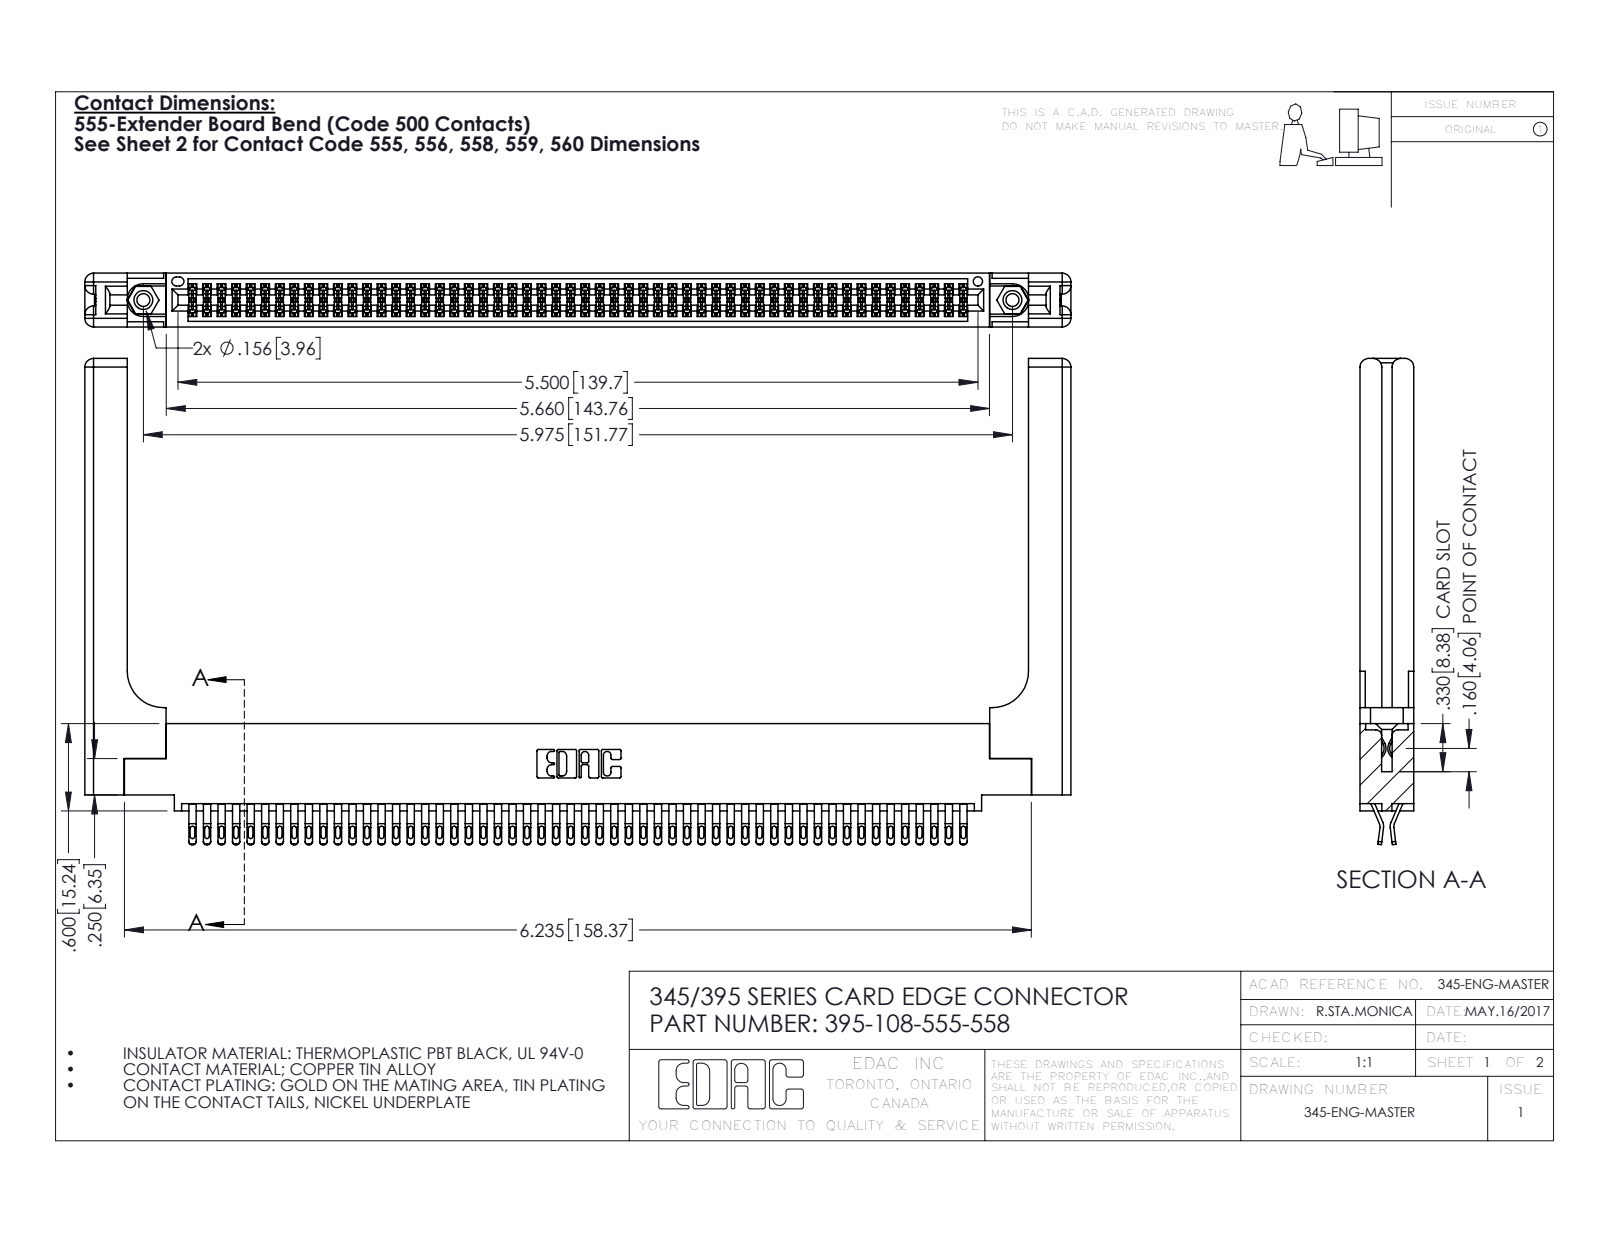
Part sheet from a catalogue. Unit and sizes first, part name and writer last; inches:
Units: inches
Overall size (bounding box): 6.779 × 3.342 × 0.37
Round holes (diameter × count): ⌀0.089 ×2, ⌀0.125 ×2, ⌀0.156 ×2, ⌀0.064 ×1
Round bosses / shafts (diameter × count): ⌀0.155 ×2
Partial cylindrical surfaces — rounded edges, fillets, slot ends (radius × count): R0.016 ×270, R0.02 ×216, R0.006 ×162, R0.01 ×22, R0.06 ×16, R0.007 ×6, R0.031 ×6, R0.026 ×3
Main face-to-face distances: 0.072, 0.298, 0.37, 0.025, 0.098, 0.272, 0.2, 0.225, 0.148, 0.15
Hole centre spacings: 0.27, 5.739, 5.975
Volume: 1.559 in³ · Surface area: 49.16 in²
Bodies: 113 solids, 6434 faces (3580 planar, 2794 cylindrical, 60 other)
Part name (STEP PRODUCT): 345 Part_0.110 Offset - 0.156 Dia-TH; 345-292-001_555 Tail; 345-220-058_345-220-058; 345-250-001_345-250-001-102 (+1 more)
STEP written by: SolidWorks 2016 (CONFIG_CONTROL_DESIGN)
